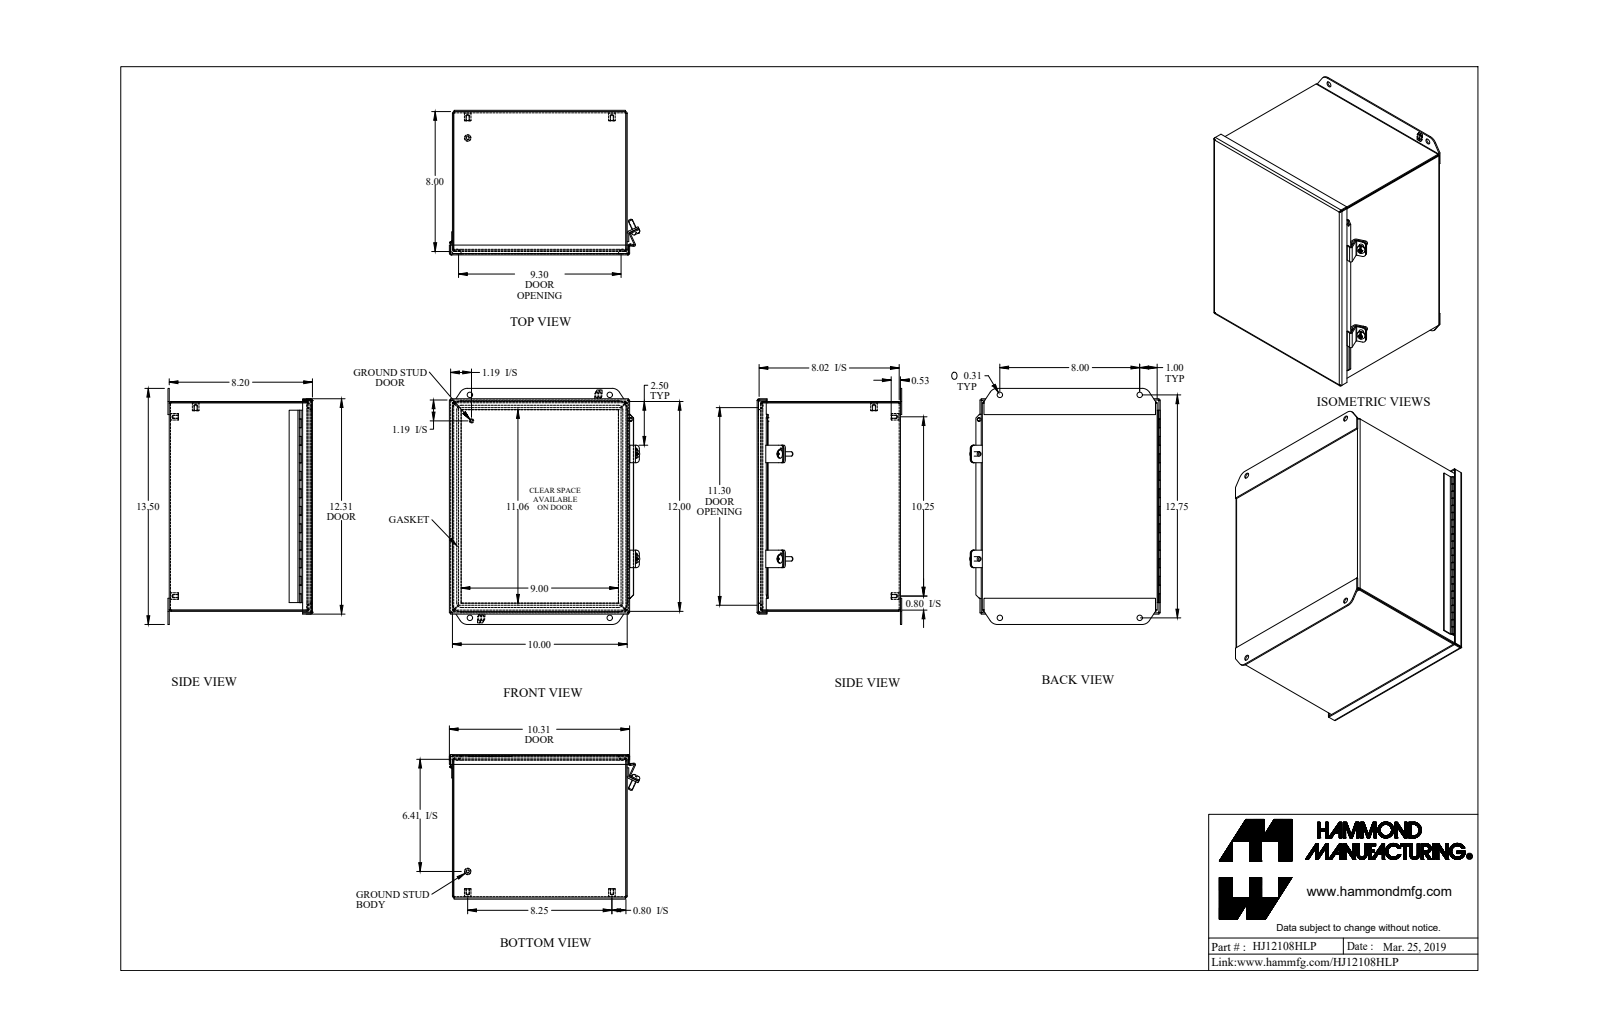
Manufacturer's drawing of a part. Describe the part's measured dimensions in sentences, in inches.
The part is named "HJ12108HLP". Its 3-D file was written by "SolidWorks 2018 (AUTOMOTIVE_DESIGN)". It is 20 solids with 773 faces: 414 planar, 232 cylindrical and 127 other. Overall it measures 13.5 by 10.896 by 8.269 inches. Its volume is 52.26 cubic inches and its surface area 1 467 square inches. Round holes: 5 of diameter 0.156, 4 of diameter 0.313, 2 of diameter 0.213, 1 of diameter 0.05. Round bosses or shafts: 5 of diameter 0.375, 3 of diameter 0.25, 2 of diameter 0.48, 1 of diameter 0.188, 1 of diameter 0.1, 1 of diameter 0.045. Partial cylindrical surfaces (rounded edges, fillets, slot ends): 16 of radius 0.25, 13 of radius 0.036, 13 of radius 0.108, 4 of radius 0.01, 4 of radius 0.141, 4 of radius 0.188, 4 of radius 0.499, 4 of radius 0.5. The main face-to-face distances are 0.072, 8.125, 9.928, 11.928, 8.197, 8.053, 9.856, 10, 12, 11.856. The hole center spacings are 1.256, 8.22, 11.501, 14.081, 8, 8.25, 10.25, 12.75.
